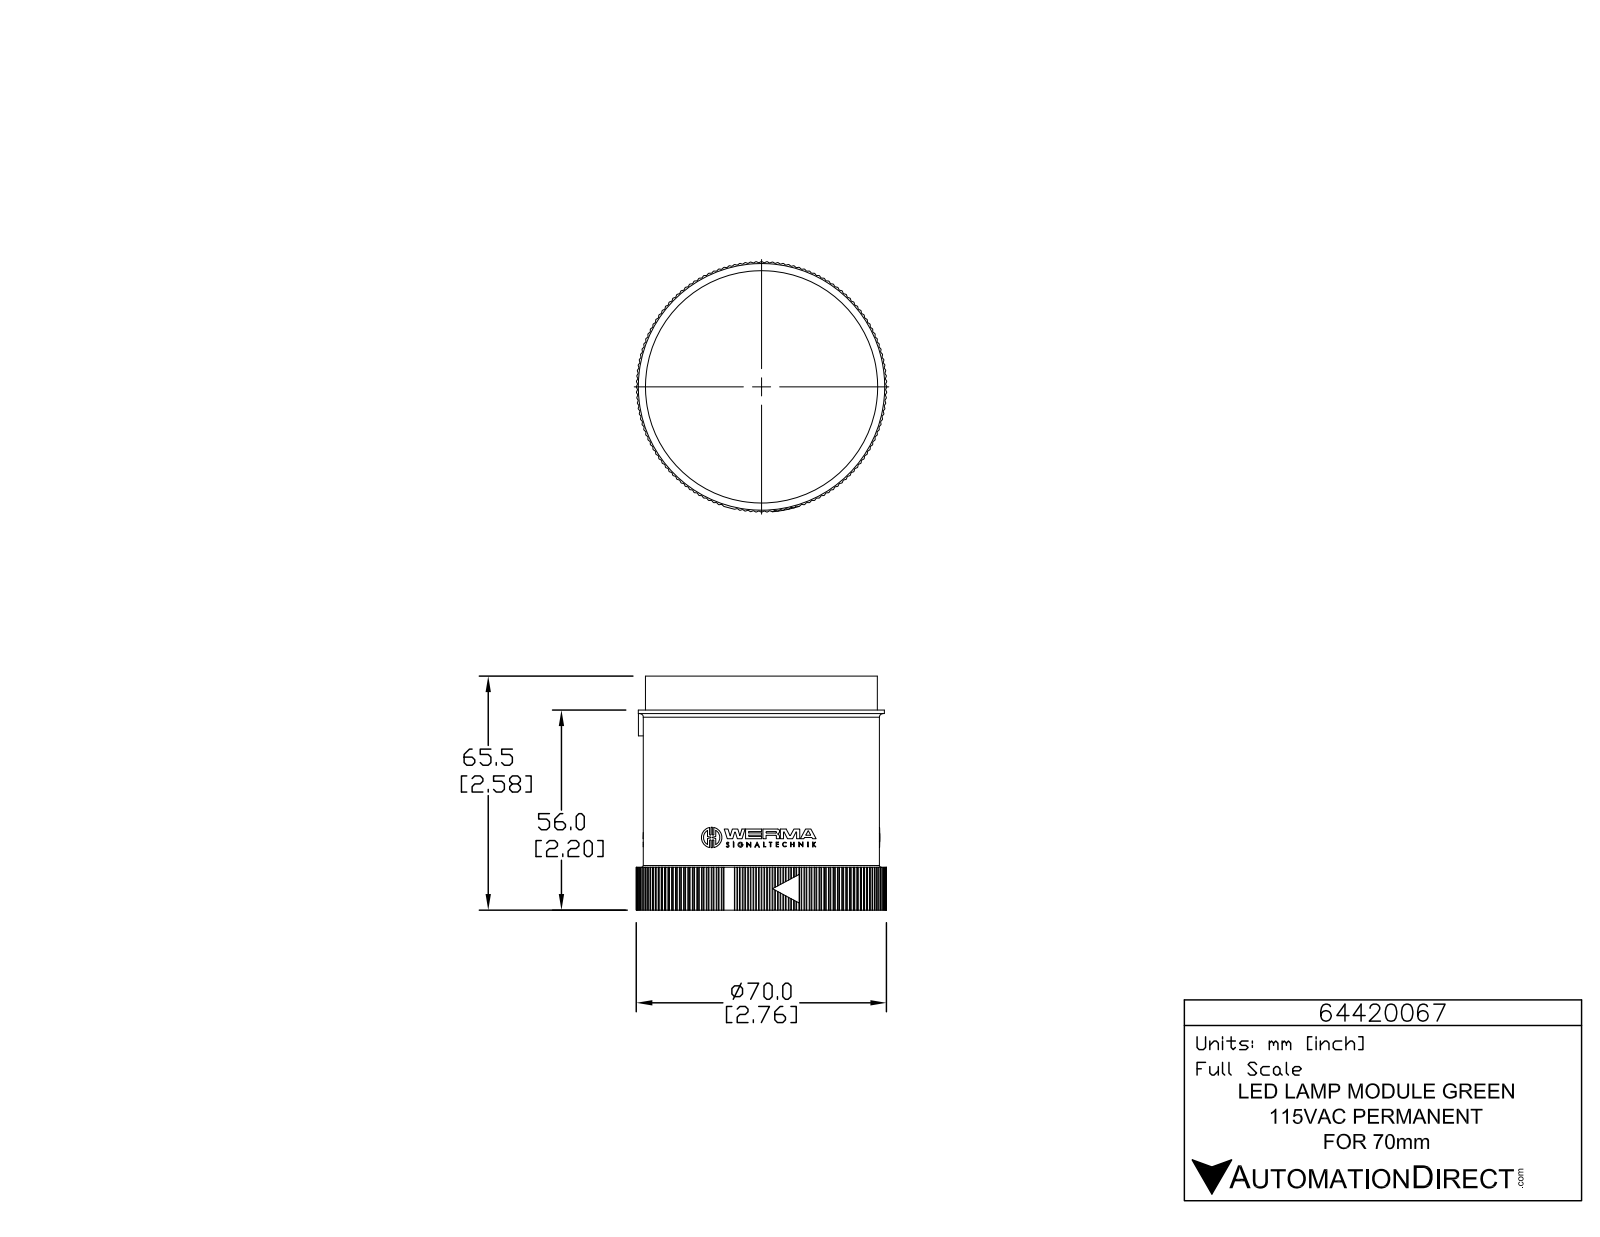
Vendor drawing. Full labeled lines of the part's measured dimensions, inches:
Part name (STEP PRODUCT): 64420067
STEP written by: SolidWorks 2015 (AUTOMOTIVE_DESIGN)
Units: inches
Bodies: 1 solid, 1400 faces (832 planar, 563 cylindrical, 5 other)
Overall size (bounding box): 2.762 × 2.762 × 2.579
Volume: 12.02 in³ · Surface area: 37.48 in²
Round holes (diameter × count): ⌀0.039 ×3, ⌀2.575 ×1
Round bosses / shafts (diameter × count): ⌀0.226 ×3, ⌀0.056 ×3, ⌀2.717 ×1, ⌀2.606 ×1, ⌀2.559 ×1
Partial cylindrical surfaces — rounded edges, fillets, slot ends (radius × count): R0.008 ×285, R0.008 ×6, R0.008 ×6, R0.008 ×6, R0.131 ×6, R0.004 ×3, R0.005 ×3, R0.008 ×3
Main face-to-face distances: 2.201, 2.451, 0.378, 2.579, 2.205, 1.827, 0.374, 2.452, 0.472, 0.094
